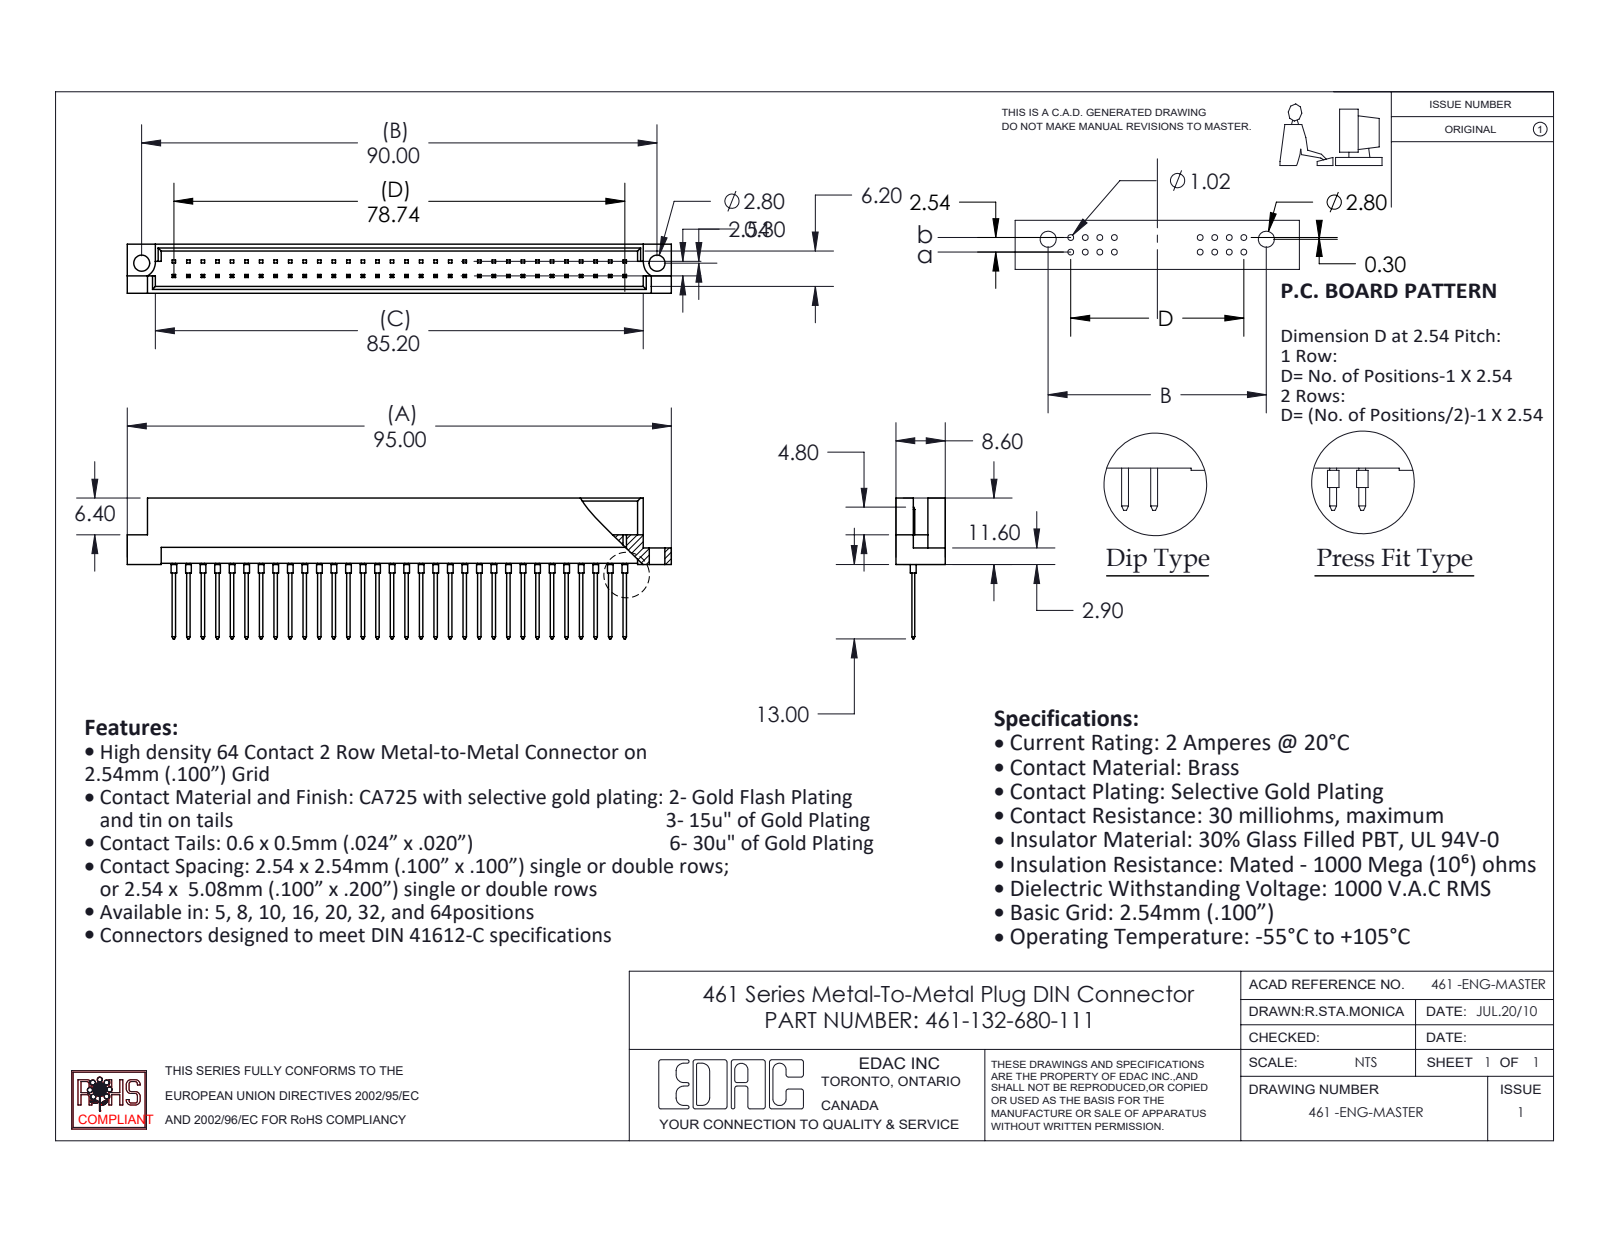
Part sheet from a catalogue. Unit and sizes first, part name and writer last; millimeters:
Units: millimetres
Overall size (bounding box): 95 × 24.6 × 8.6
Round holes (diameter × count): ⌀2.8 ×2
Round bosses / shafts (diameter × count): ⌀1 ×32
Partial cylindrical surfaces — rounded edges, fillets, slot ends (radius × count): R2.8 ×2
Main face-to-face distances: 1.2, 7.4, 8.6, 6.2, 3.28, 5.32, 2.08, 4.12, 2.78, 5.82
Hole centre spacings: 90
Volume: 4 897 mm³ · Surface area: 7 355 mm²
Bodies: 33 solids, 1009 faces (938 planar, 71 cylindrical, 0 other)
Part name (STEP PRODUCT): 461 Part_64; 461-132-680-111; 461-290_80
STEP written by: SolidWorks 2020 (CONFIG_CONTROL_DESIGN)
